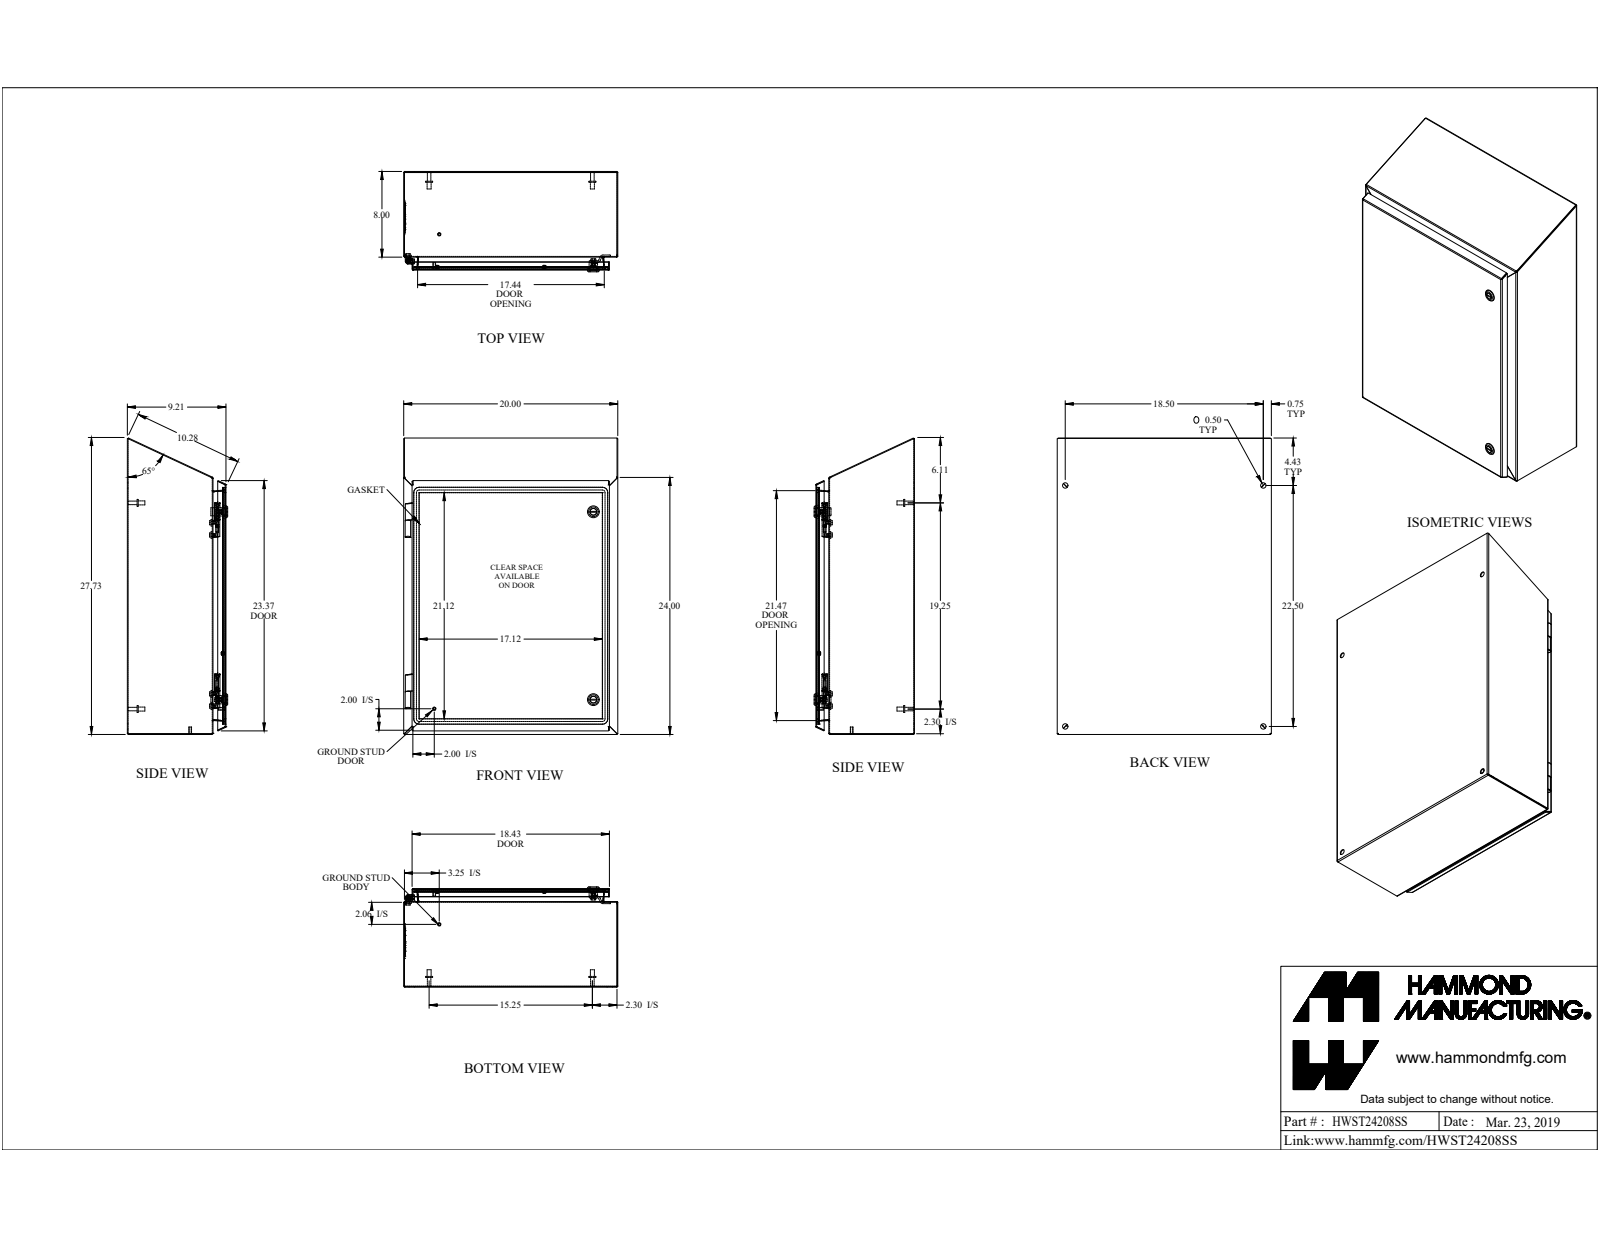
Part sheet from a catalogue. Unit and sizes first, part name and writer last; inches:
Units: inches
Overall size (bounding box): 27.684 × 20 × 9.37
Round holes (diameter × count): ⌀0.194 ×8, ⌀0.5 ×6, ⌀0.24 ×4, ⌀0.275 ×4, ⌀0.13 ×2, ⌀0.197 ×2, ⌀0.387 ×2, ⌀0.63 ×2, ⌀0.768 ×2, ⌀0.24 ×1, ⌀3.5 ×1
Round bosses / shafts (diameter × count): ⌀0.226 ×8, ⌀0.625 ×6, ⌀0.65 ×4, ⌀0.375 ×4, ⌀0.332 ×4, ⌀0.25 ×4, ⌀0.236 ×3, ⌀1.1 ×2
Partial cylindrical surfaces — rounded edges, fillets, slot ends (radius × count): R0.25 ×24, R0.039 ×16, R0.108 ×16, R0.012 ×12, R0.036 ×12, R0.125 ×12, R0.108 ×9, R0.036 ×7
Main face-to-face distances: 0.072, 9.066, 9.138, 0.072, 9.138, 9.21, 19.928, 19.856, 20, 7.928
Hole centre spacings: 1.142, 15.979, 14.837, 15.98, 17.12, 18.5, 22.5, 29.129
Volume: 159.6 in³ · Surface area: 4 313 in²
Bodies: 43 solids, 1037 faces (631 planar, 292 cylindrical, 114 other)
Part name (STEP PRODUCT): HWST24208S16
STEP written by: SolidWorks 2019 (AUTOMOTIVE_DESIGN)
